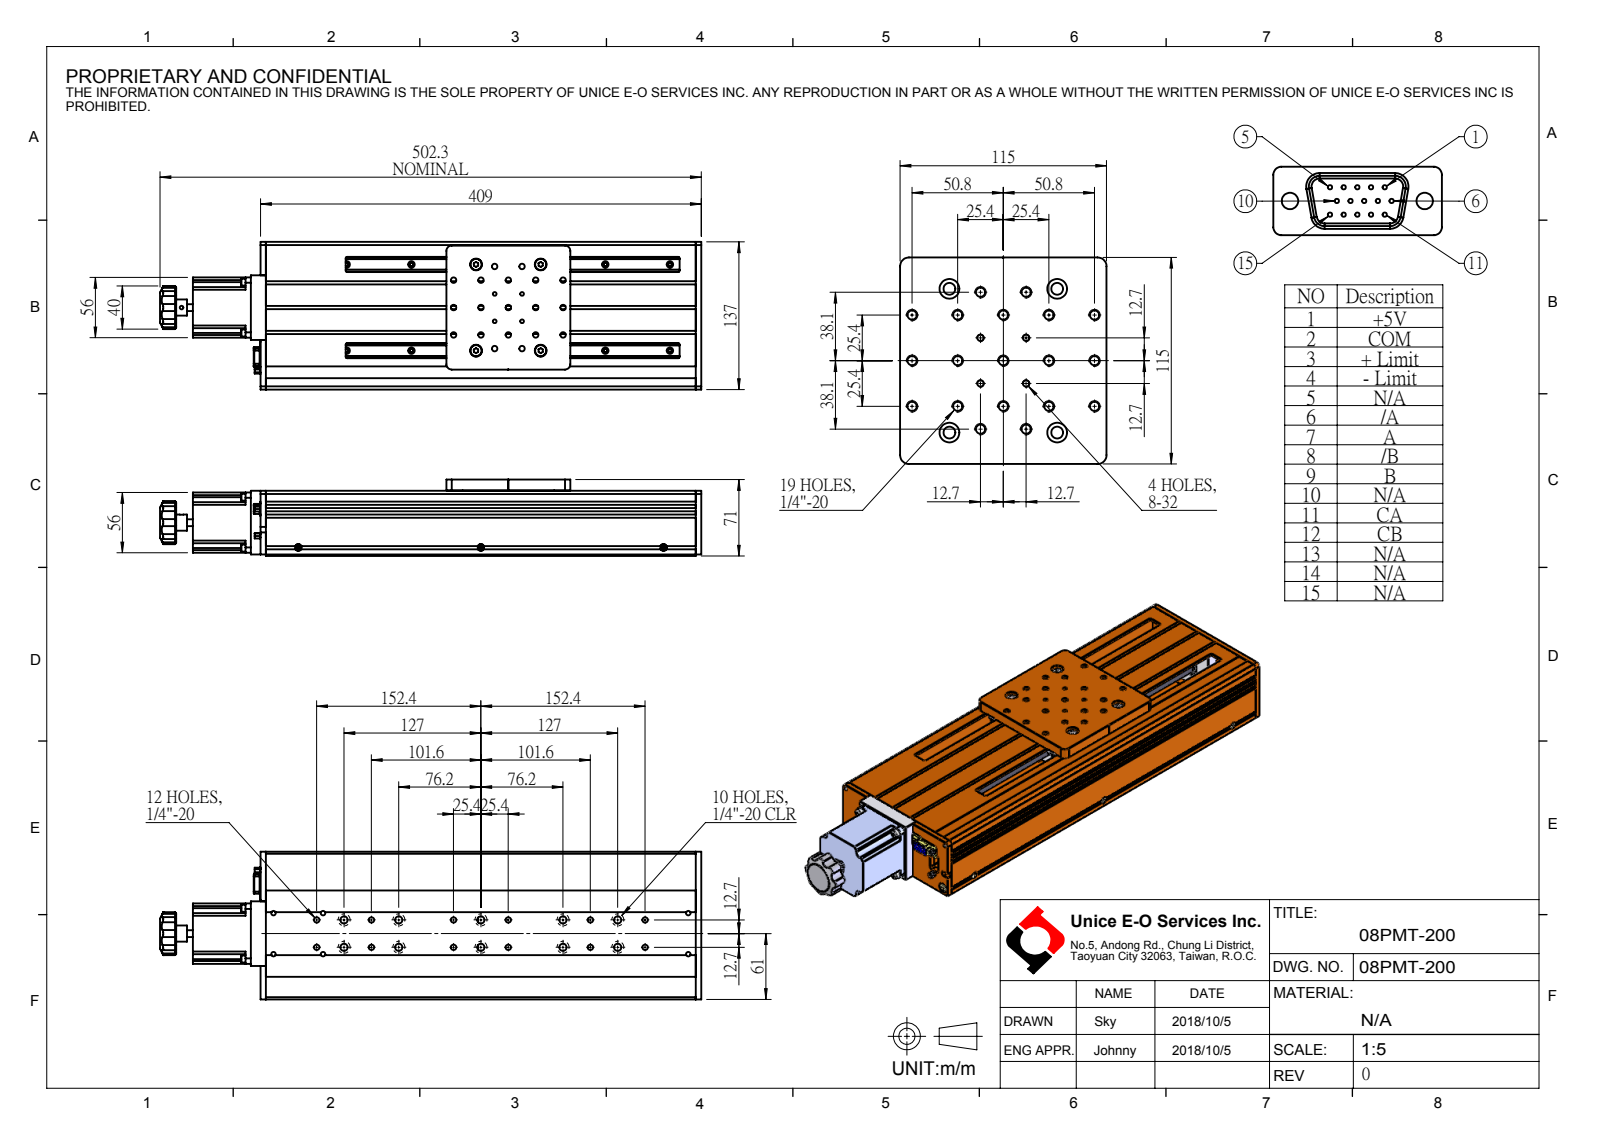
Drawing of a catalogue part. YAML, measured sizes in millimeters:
part_name: "08PMT-200"
step_written_by: "SolidWorks 2016 (AUTOMOTIVE_DESIGN)"
units: millimeters
bodies: {solids: 0, faces: 811, planar: 387, cylindrical: 305, other: 119}
overall_size: [502.3, 137, 71]
round_holes:
  - {diameter: 5.11, count: 31}
  - {diameter: 0.8, count: 11}
  - {diameter: 6.76, count: 10}
  - {diameter: 11.11, count: 10}
  - {diameter: 1, count: 6}
  - {diameter: 4.2, count: 6}
  - {diameter: 3.45, count: 4}
  - {diameter: 11, count: 4}
  - {diameter: 2, count: 2}
  - {diameter: 2.5, count: 2}
  - {diameter: 3.3, count: 2}
  - {diameter: 18, count: 1}
round_bosses_or_shafts:
  - {diameter: 6.5, count: 4}
  - {diameter: 5.8, count: 3}
  - {diameter: 7.7, count: 2}
  - {diameter: 3, count: 2}
  - {diameter: 16, count: 1}
  - {diameter: 15, count: 1}
  - {diameter: 6.35, count: 1}
  - {diameter: 1.2, count: 1}
partial_cylinders:
  - {radius: 1.5, count: 10}
  - {radius: 2, count: 8}
  - {radius: 4, count: 8}
  - {radius: 5, count: 8}
  - {radius: 7.41, count: 8}
  - {radius: 0.5, count: 7}
  - {radius: 4.5, count: 4}
  - {radius: 3, count: 2}
face_to_face_distances: [2, 60.5, 135, 133, 10.5, 1.5, 9, 59, 137, 1.7]
hole_center_spacings: [25.4, 35.92, 56.8, 50.8, 76.2, 80.32, 101.6, 104.73]
